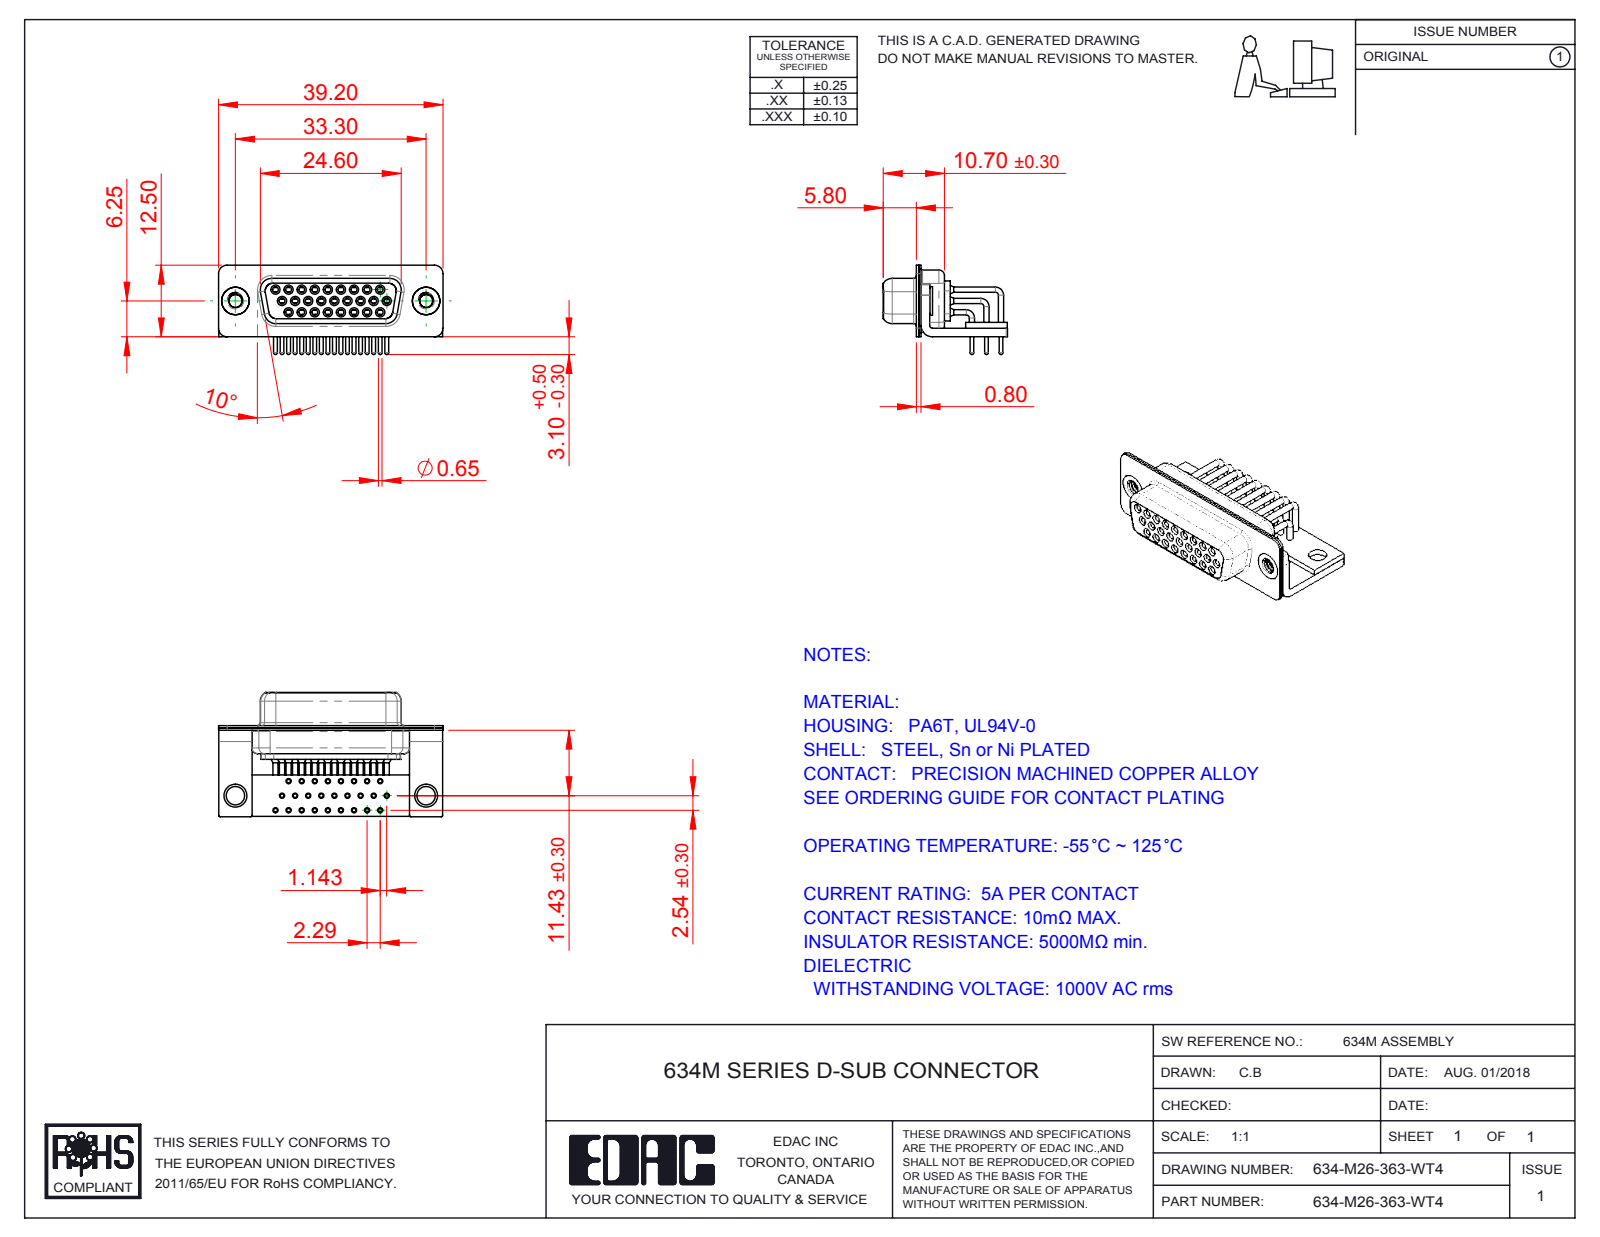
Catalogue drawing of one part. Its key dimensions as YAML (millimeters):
part_name: "634M 4-40 Threaded Rivet_Stabilizer; 634M Contact Row 3; 634M Stabilizer Bracket; 634M Contact Row 2 (+6 more)"
step_written_by: "SolidWorks 2016 (CONFIG_CONTROL_DESIGN)"
units: millimeters
bodies: {solids: 34, faces: 1759, planar: 483, cylindrical: 809, other: 467}
overall_size: [39.2, 21.7, 15.6]
volume: 3063
surface_area: 9770
round_holes:
  - {diameter: 0.9, count: 26}
  - {diameter: 1, count: 26}
  - {diameter: 1.1, count: 26}
  - {diameter: 1.7, count: 26}
  - {diameter: 1.8, count: 26}
  - {diameter: 2, count: 26}
  - {diameter: 2.26, count: 2}
  - {diameter: 3.2, count: 2}
  - {diameter: 4, count: 2}
  - {diameter: 4.8, count: 2}
round_bosses_or_shafts:
  - {diameter: 0.9, count: 27}
  - {diameter: 1.6, count: 26}
  - {diameter: 1.5, count: 26}
  - {diameter: 0.65, count: 26}
  - {diameter: 5, count: 2}
  - {diameter: 4.9, count: 2}
  - {diameter: 2, count: 1}
partial_cylinders:
  - {radius: 0.25, count: 16}
  - {radius: 1.5, count: 16}
  - {radius: 2, count: 13}
  - {radius: 1.35, count: 8}
  - {radius: 1.6, count: 8}
  - {radius: 0.5, count: 5}
  - {radius: 0.6, count: 4}
  - {radius: 0.65, count: 4}
face_to_face_distances: [0.4, 2.3, 0.8, 1, 1.5, 1.9, 9.35, 1.45, 8.95, 0.85]
hole_center_spacings: [4.57, 2.29, 2.28, 3.96, 6.05, 6.86, 4.27, 2.78]
